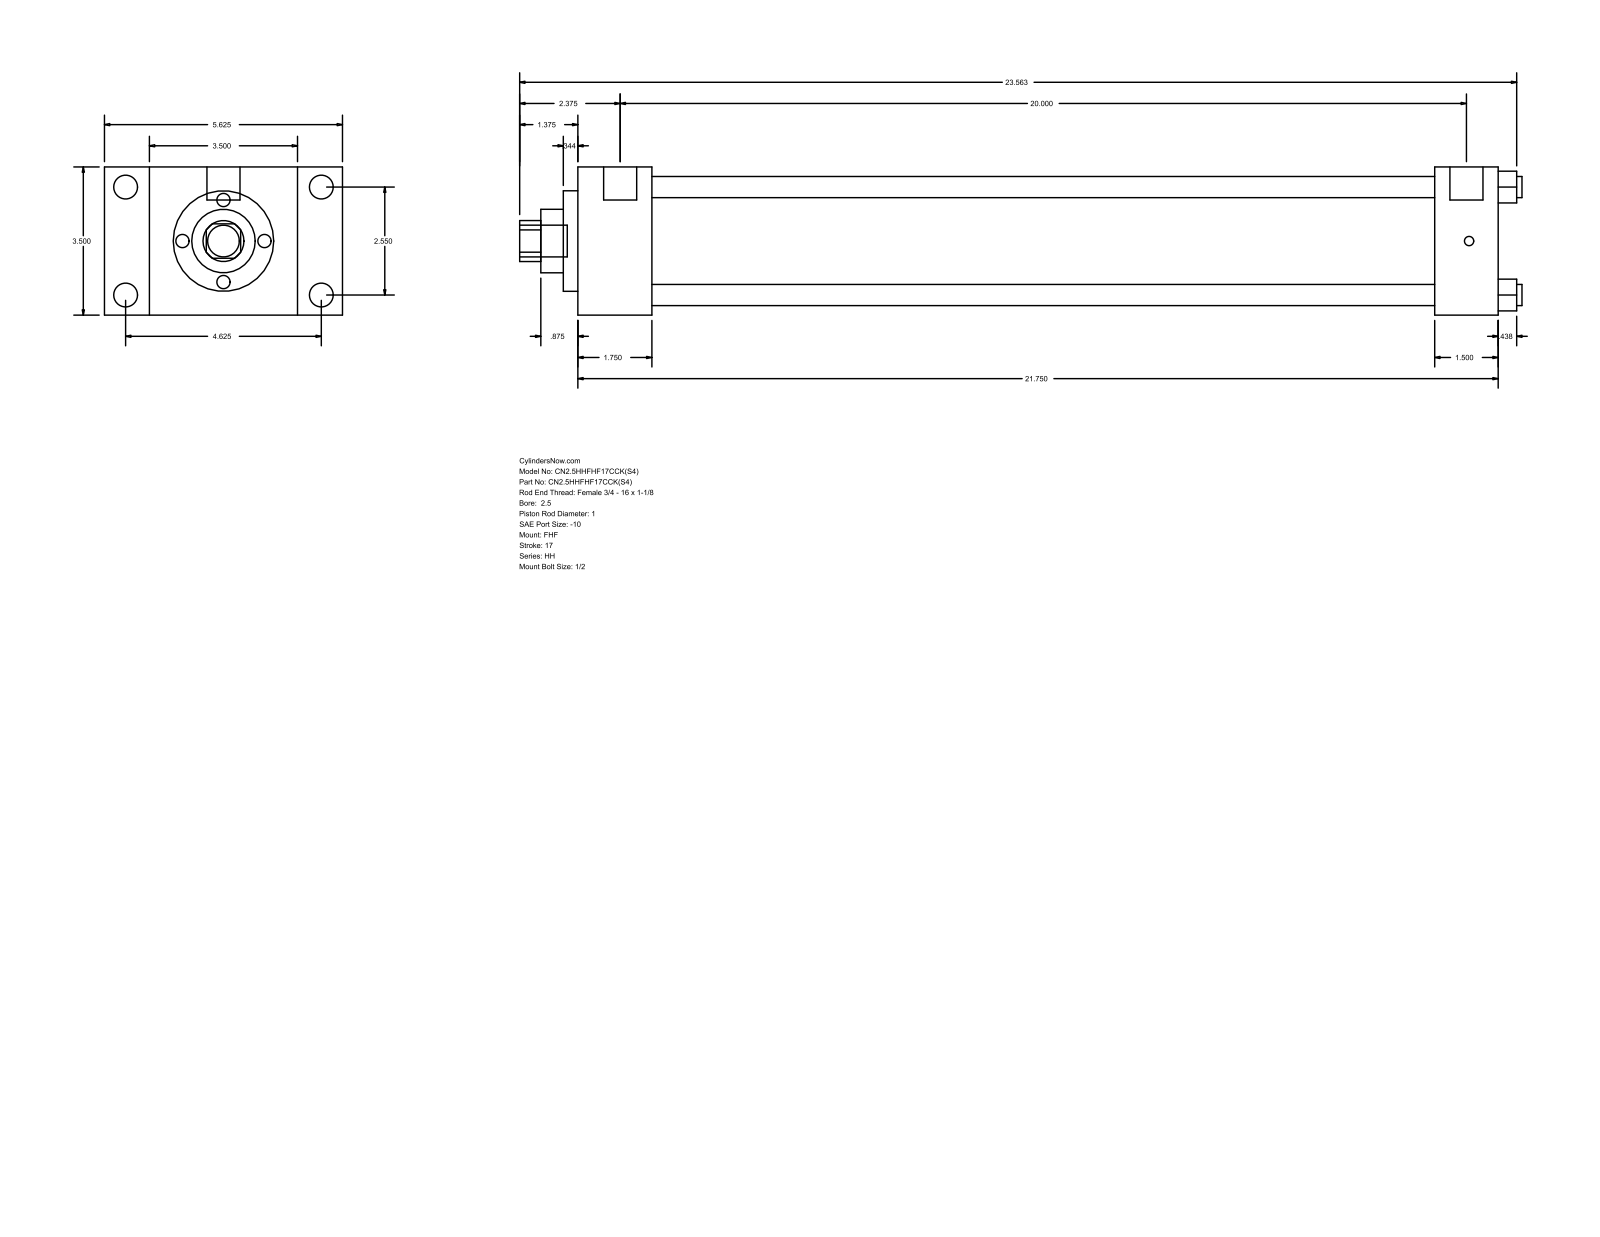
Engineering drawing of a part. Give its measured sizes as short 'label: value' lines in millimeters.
name: HH_FHF__0250_1
written by: GSSL Pune (CONFIG_CONTROL_DESIGN)
unit: mm
bodies: 0 solids, 90 faces (61 planar, 29 cylindrical, 0 other)
size: 601.66 × 142.88 × 88.9
holes: 4× ⌀12.7, 1× ⌀25.4, 1× ⌀38.1, 1× ⌀60.33, 1× ⌀73.03
bosses: 4× ⌀14.3, 4× ⌀5.56, 2× ⌀19.84, 1× ⌀19.05
rounds: 1× R12.29
face distances: 88.9, 44.46, 26.99, 115.89, 552.46, 508, 142.88, 514.35, 469.89, 38.11
hole spacings: 45.79, 64.76, 91.58
